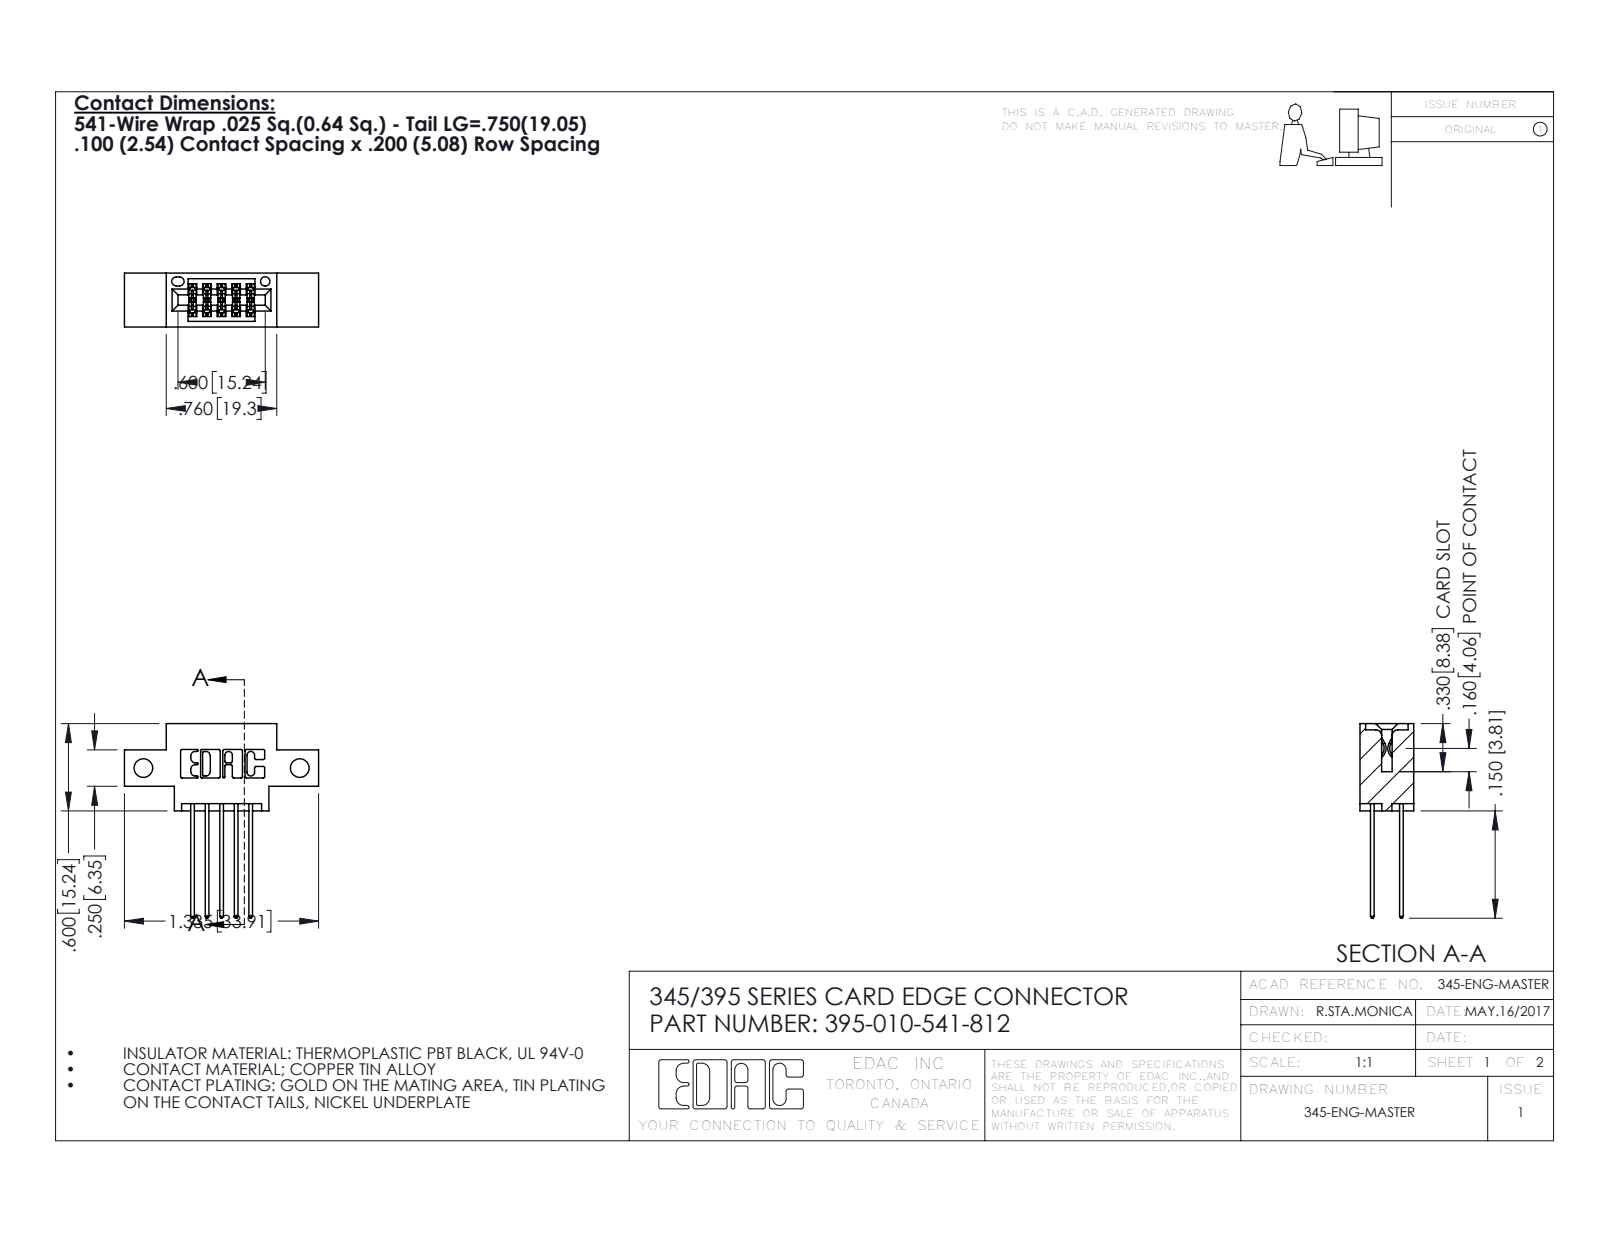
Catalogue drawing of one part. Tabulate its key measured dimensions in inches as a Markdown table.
| quantity | value |
| --- | --- |
| part name | 395-010-541-812; 345-292-001_345-293-141; 345 Part_0.170 Offset - Side Mount |
| STEP written by | SolidWorks 2016 (CONFIG_CONTROL_DESIGN) |
| units | inches |
| bodies | 11 solids, 630 faces (414 planar, 216 cylindrical, 0 other) |
| overall size | 1.337 × 1.335 × 0.37 |
| volume | 0.171 in³ |
| surface area | 5.751 in² |
| round holes (diameter × count) | 0.128 × 2, 0.064 × 1 |
| partial cylindrical surfaces (radius × count) | 0.01 × 22, 0.006 × 15, 0.01 × 10, 0.007 × 6, 0.031 × 6, 0.026 × 3, 0.014 × 2, 0.019 × 2 |
| main face-to-face distances | 0.2, 0.072, 0.298, 0.37, 0.1, 0.098, 0.272, 0.025, 0.225, 0.25 |
| hole center spacings | 1.075 |
